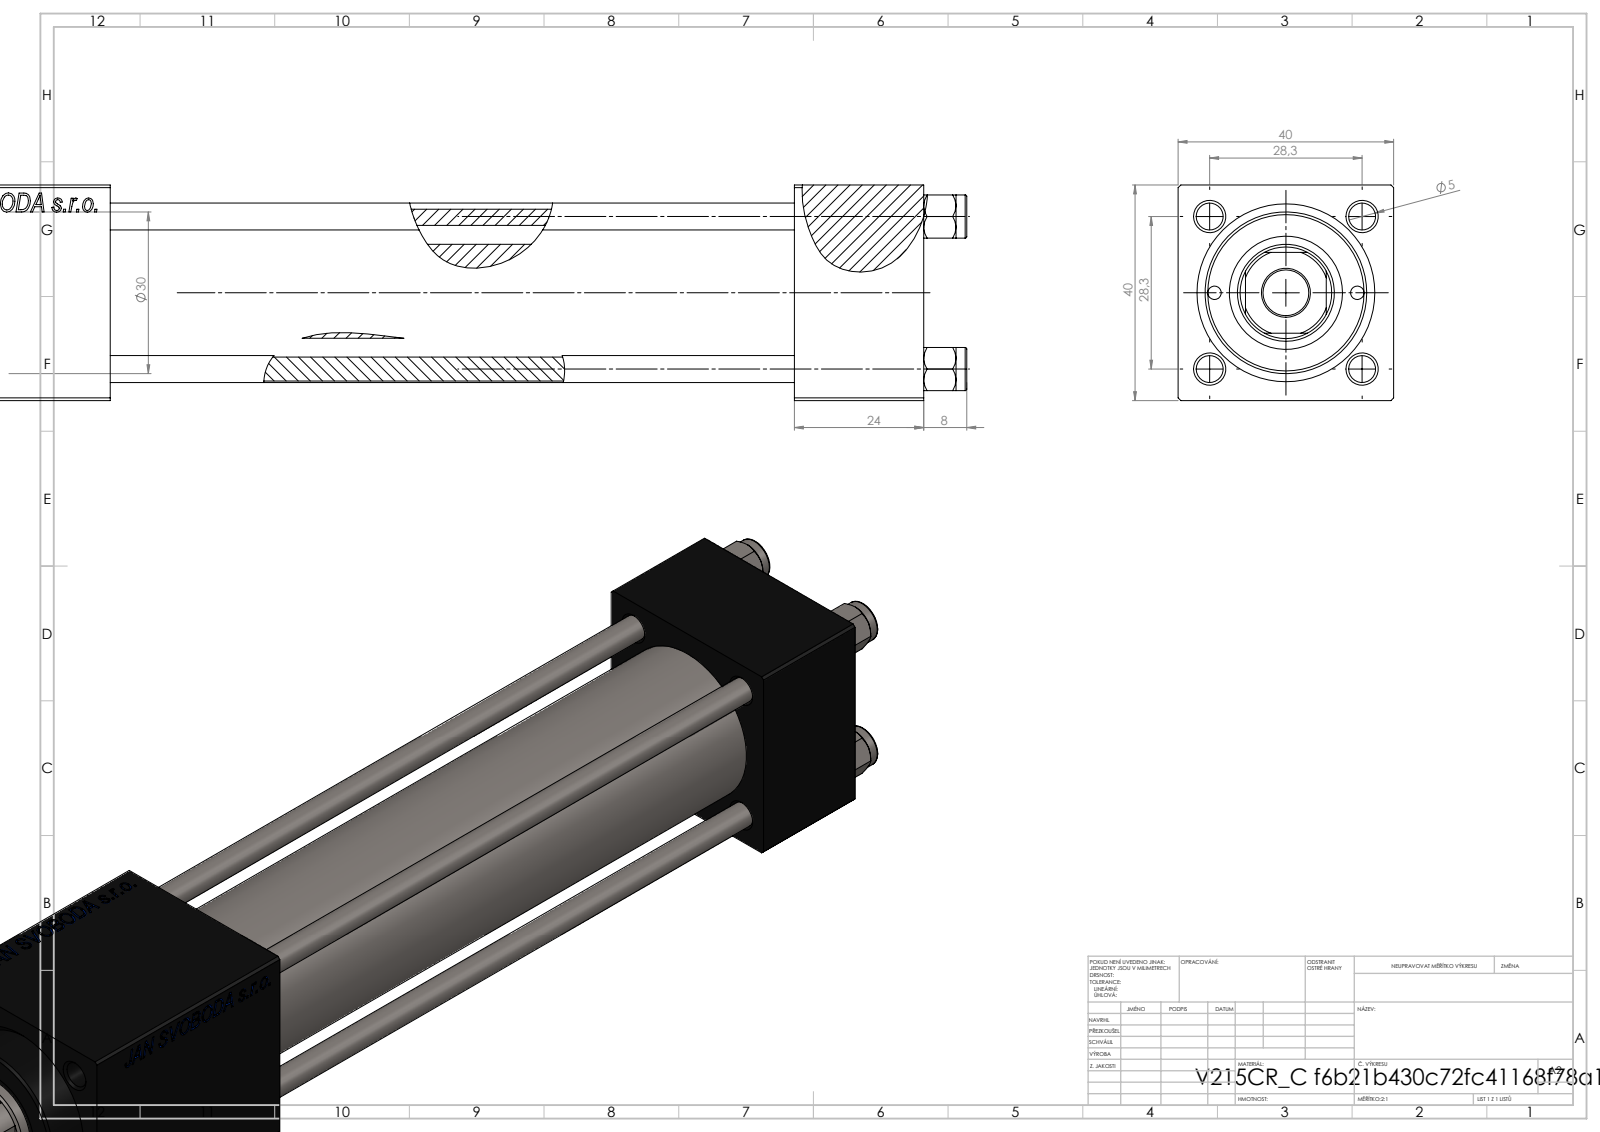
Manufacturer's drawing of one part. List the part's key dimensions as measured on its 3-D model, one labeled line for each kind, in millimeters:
Part name (STEP PRODUCT): V215CR_C_TYCINKA; NUT_M5_C; V215_VC_A; V215CR_C_Body (+1 more)
STEP written by: SolidWorks 2019 (CONFIG_CONTROL_DESIGN)
Units: millimetres
Bodies: 11 solids, 1150 faces (526 planar, 88 cylindrical, 536 other)
Overall size (bounding box): 222 × 40 × 40
Volume: 197 631 mm³ · Surface area: 80 530 mm²
Round holes (diameter × count): ⌀5 ×4, ⌀20 ×3, ⌀2.5 ×2, ⌀7 ×2, ⌀13.16 ×2, ⌀8.5 ×1, ⌀18 ×1, ⌀21 ×1, ⌀25 ×1, ⌀30 ×1
Round bosses / shafts (diameter × count): ⌀8 ×4, ⌀31 ×1
Partial cylindrical surfaces — rounded edges, fillets, slot ends (radius × count): R8.5 ×1
Main face-to-face distances: 40, 24, 151, 127, 170.3, 146.3, 19.3, 48, 199, 175
Hole centre spacings: 14.18, 20.01, 28.3, 30.84, 13.25, 40.02, 26.5, 152
